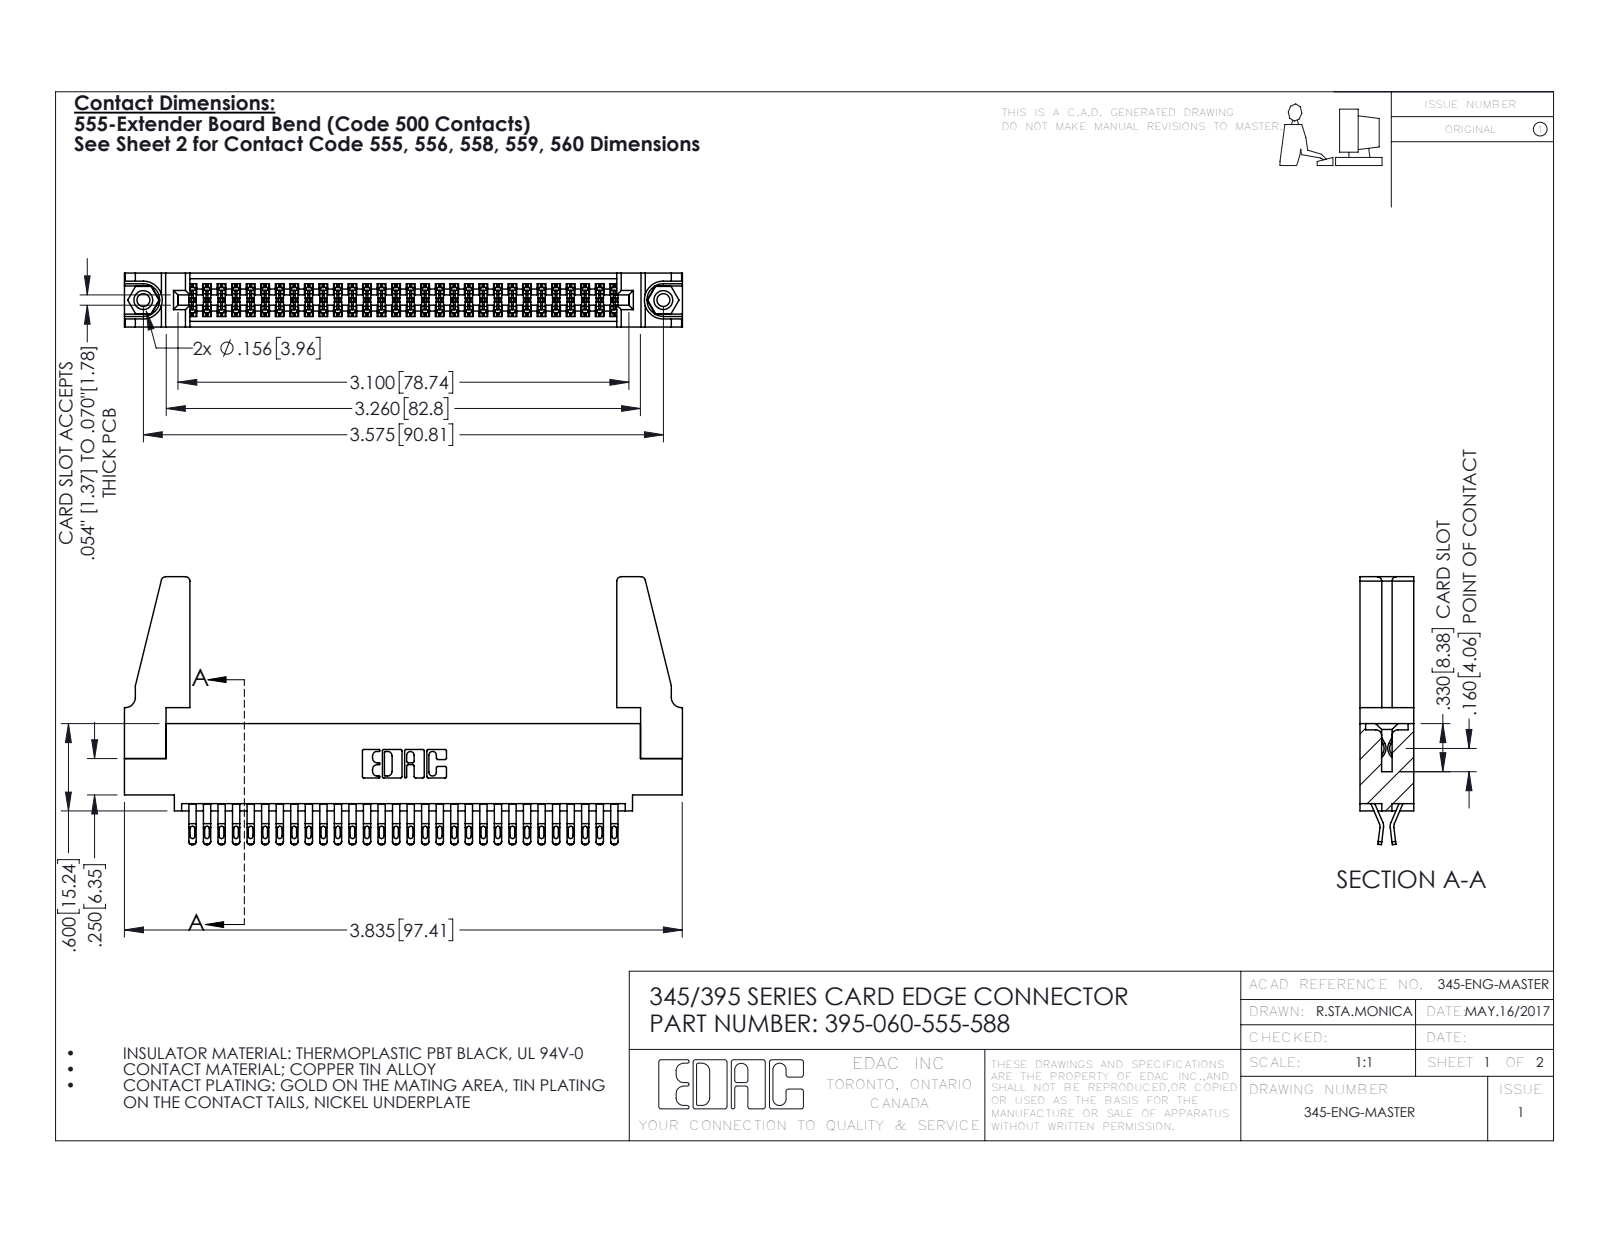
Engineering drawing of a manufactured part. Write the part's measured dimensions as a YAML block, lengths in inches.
part_name: "345-292-001_555 Tail; 345 Part_0.110 Offset - 0.156 Dia-TH; 345-220-078_345-220-088; 395-060-555-588 (+1 more)"
step_written_by: "SolidWorks 2016 (CONFIG_CONTROL_DESIGN)"
units: inches
bodies: {solids: 65, faces: 3614, planar: 2016, cylindrical: 1582, other: 16}
overall_size: [3.836, 1.842, 0.37]
volume: 0.775
surface_area: 27.22
round_holes:
  - {diameter: 0.089, count: 2}
  - {diameter: 0.125, count: 2}
  - {diameter: 0.156, count: 2}
  - {diameter: 0.064, count: 1}
round_bosses_or_shafts:
  - {diameter: 0.155, count: 2}
partial_cylinders:
  - {radius: 0.016, count: 150}
  - {radius: 0.02, count: 120}
  - {radius: 0.006, count: 90}
  - {radius: 0.01, count: 22}
  - {radius: 0.03, count: 8}
  - {radius: 0.007, count: 6}
  - {radius: 0.031, count: 6}
  - {radius: 0.026, count: 3}
face_to_face_distances: [0.072, 0.298, 0.37, 0.025, 0.2, 0.098, 0.272, 0.225, 0.175, 0.149]
hole_center_spacings: [0.27, 3.34, 3.575]
